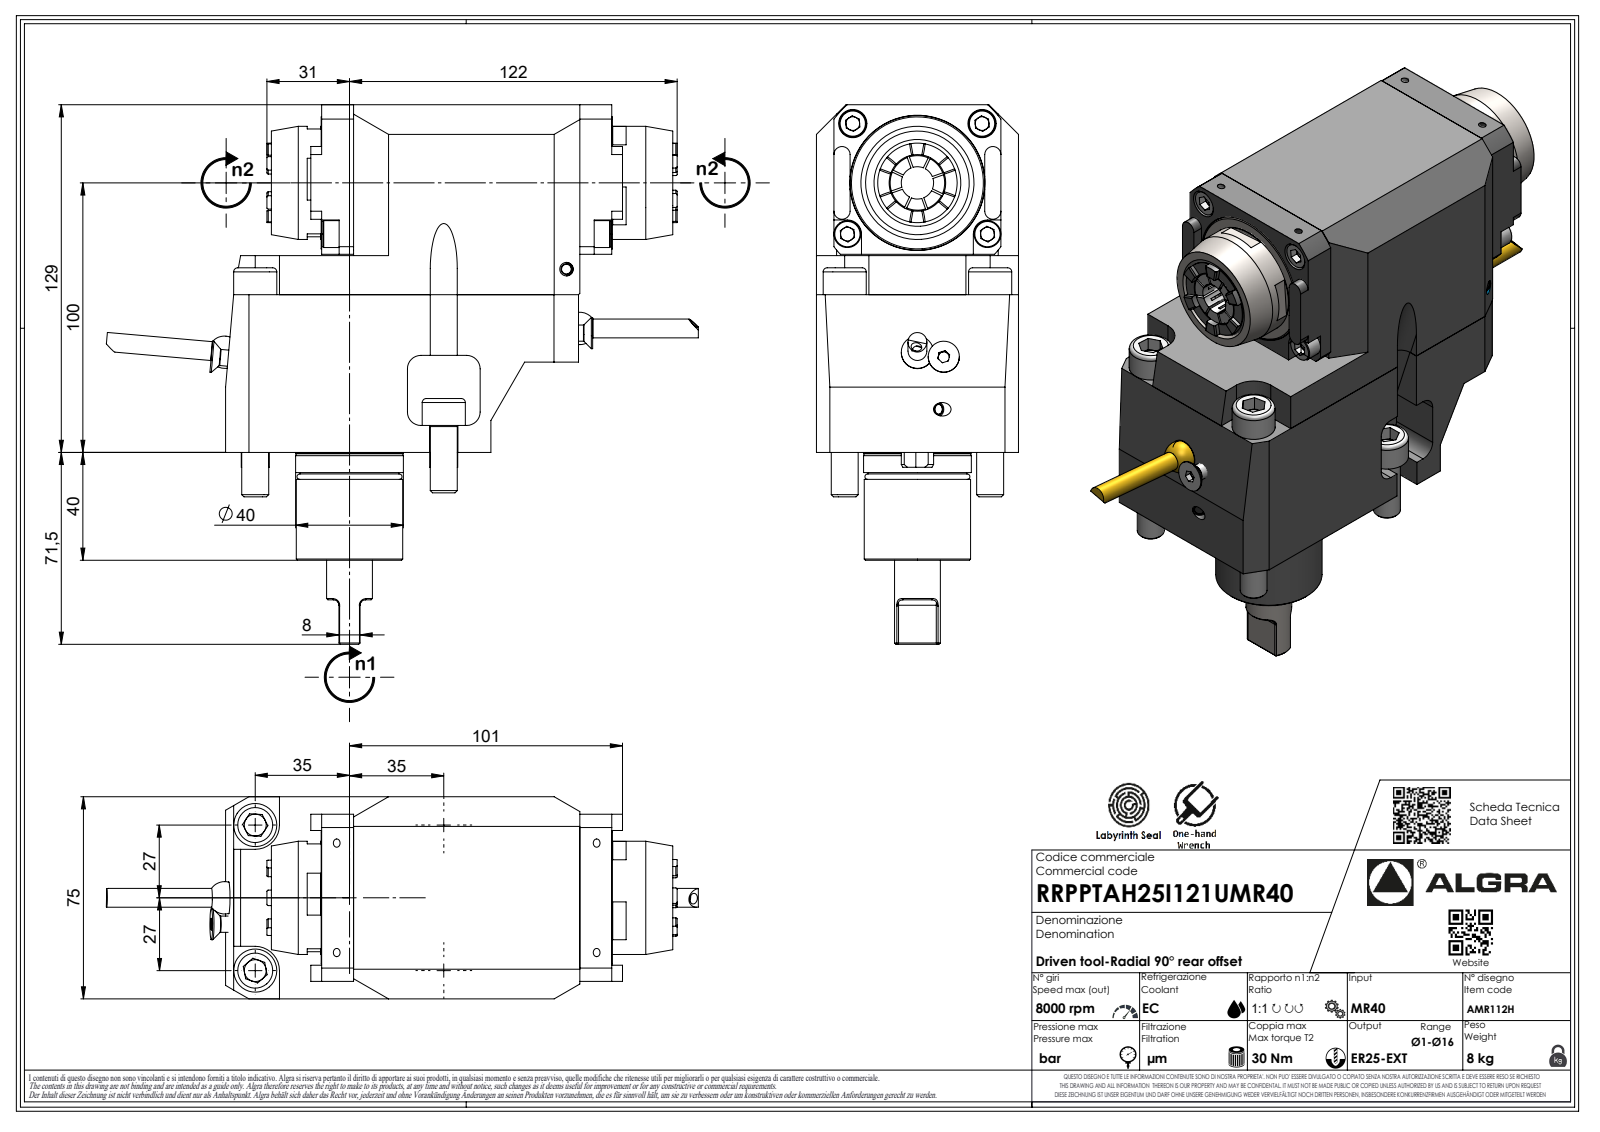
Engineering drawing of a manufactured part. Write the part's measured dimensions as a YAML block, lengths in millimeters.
part_name: "RRPPTAH25I121UMR40"
step_written_by: "SolidWorks 2023 (AUTOMOTIVE_DESIGN)"
units: millimeters
bodies: {solids: 1, faces: 574, planar: 392, cylindrical: 80, other: 102}
overall_size: [219.77, 200.2, 75]
volume: 1170000
surface_area: 85098
round_holes:
  - {diameter: 4, count: 2}
  - {diameter: 2.1, count: 1}
  - {diameter: 5, count: 1}
round_bosses_or_shafts:
  - {diameter: 10, count: 4}
  - {diameter: 16, count: 2}
  - {diameter: 7, count: 2}
  - {diameter: 42, count: 1}
  - {diameter: 40, count: 1}
  - {diameter: 39.6, count: 1}
  - {diameter: 39.5, count: 1}
  - {diameter: 38.63, count: 1}
partial_cylinders:
  - {radius: 2, count: 8}
  - {radius: 0.33, count: 7}
  - {radius: 0.52, count: 7}
  - {radius: 3.7, count: 7}
  - {radius: 3, count: 4}
  - {radius: 6, count: 2}
  - {radius: 9, count: 2}
  - {radius: 0.21, count: 1}
face_to_face_distances: [75, 129, 68.5, 56, 6.5, 73, 0.5, 73.5, 40, 95.5]
